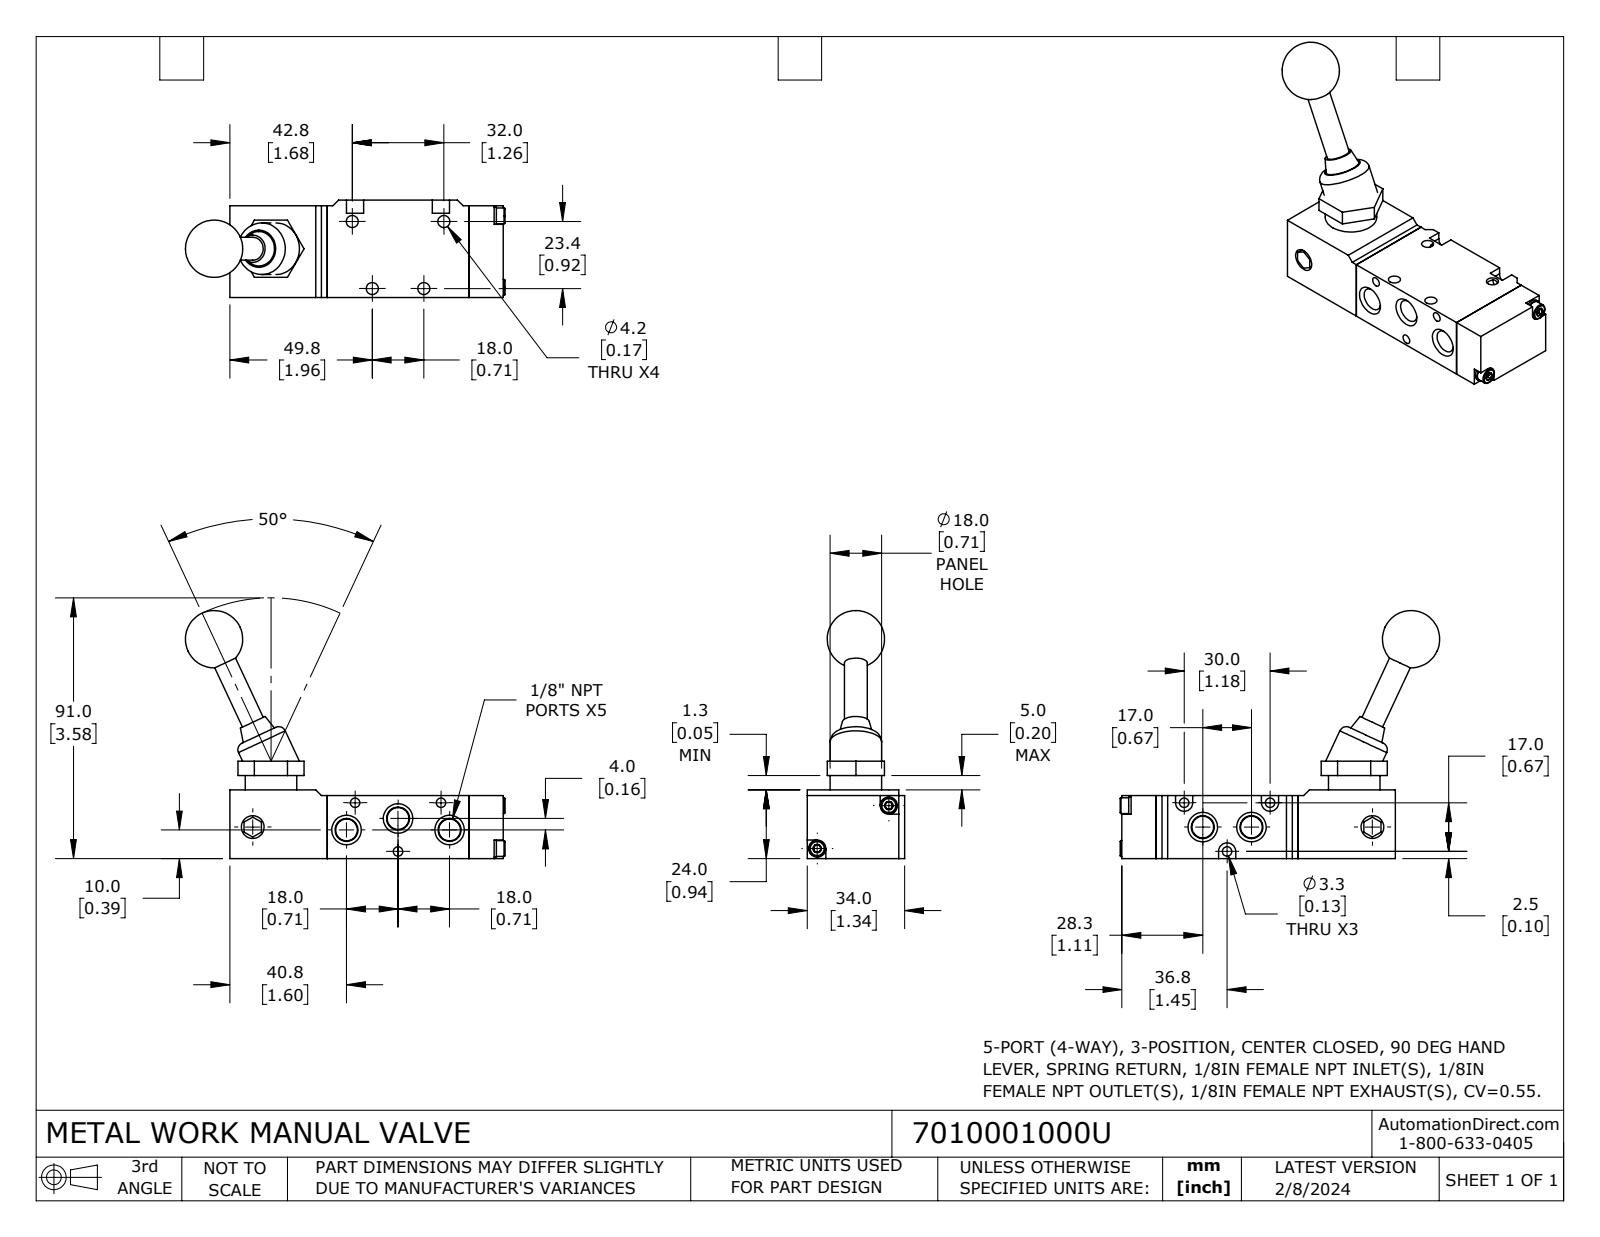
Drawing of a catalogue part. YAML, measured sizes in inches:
part_name: "7010001000U"
step_written_by: "SolidWorks 2023 (CONFIG_CONTROL_DESIGN)"
units: inches
bodies: {solids: 8, faces: 208, planar: 105, cylindrical: 49, other: 54}
overall_size: [4.393, 3.409, 1.339]
volume: 4.828
surface_area: 34.88
round_holes:
  - {diameter: 0.165, count: 4}
  - {diameter: 0.13, count: 3}
  - {diameter: 0.118, count: 2}
  - {diameter: 0.313, count: 1}
round_bosses_or_shafts:
  - {diameter: 0.709, count: 2}
  - {diameter: 0.236, count: 2}
  - {diameter: 0.217, count: 2}
  - {diameter: 0.315, count: 1}
partial_cylinders:
  - {radius: 0.118, count: 3}
face_to_face_distances: [0.866, 1.339, 1.949, 0.079, 1.26, 0.472, 3.287, 0.945, 2.421, 3.76]
hole_center_spacings: [0.893, 0.961, 1.348, 0.709, 1.148, 1.181, 1.26, 1.447]
